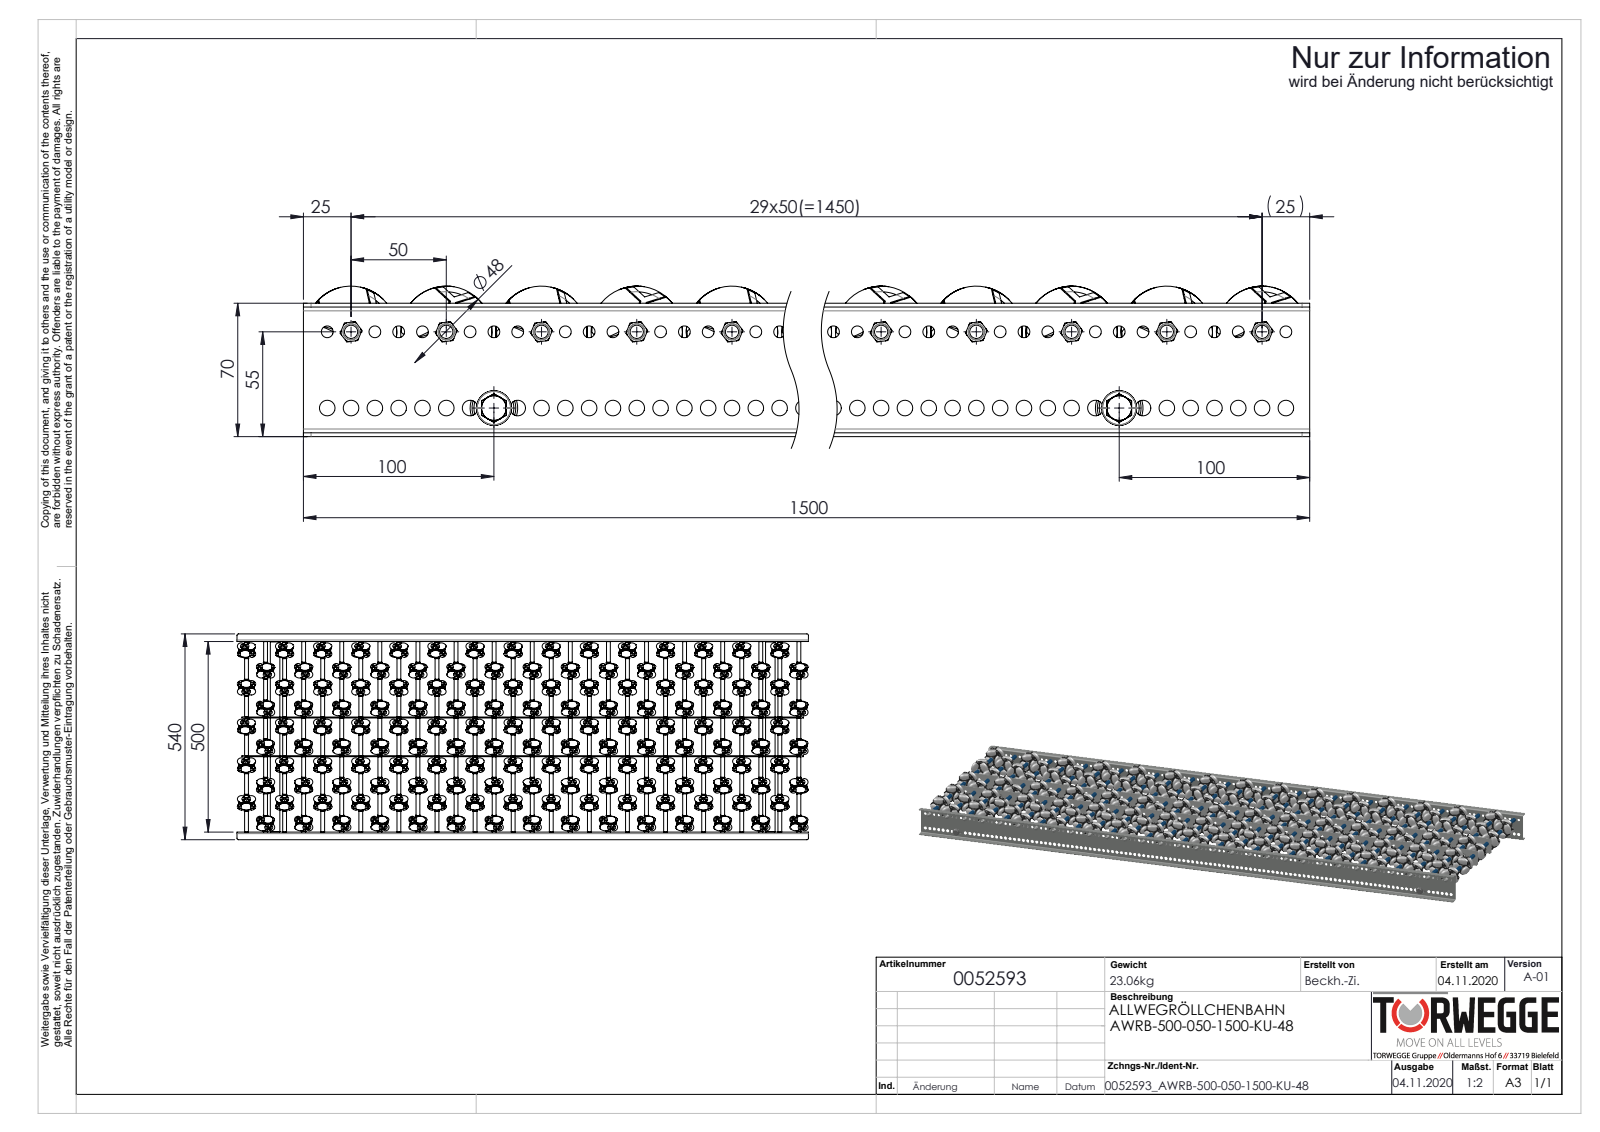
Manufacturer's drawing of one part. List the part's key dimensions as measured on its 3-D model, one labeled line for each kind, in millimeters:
Part name (STEP PRODUCT): AWR48_Röllchen; 0019719_Gewindestange-M6_L=520; 0019730_Tragrollenrohr-Ø10x1,75KU_KFG_0019730_L=54; AWR-Achse-für-Konfiguration_L500 (+8 more)
STEP written by: SolidWorks 2020 (AUTOMOTIVE_DESIGN)
Units: millimetres
Bodies: 2504 solids, 44268 faces (15372 planar, 17152 cylindrical, 11744 other)
Overall size (bounding box): 1500 × 540 × 79
Volume: 8 257 000 mm³ · Surface area: 5 570 000 mm²
Round holes (diameter × count): ⌀3.7 ×900, ⌀4.2 ×900, ⌀6.2 ×119, ⌀8.2 ×119, ⌀6.5 ×59, ⌀4.92 ×30, ⌀8.4 ×30, ⌀6.8 ×2, ⌀21 ×2
Round bosses / shafts (diameter × count): ⌀4 ×900, ⌀3.7 ×781, ⌀8 ×32, ⌀42 ×30, ⌀11 ×30, ⌀10 ×30, ⌀7 ×30, ⌀6 ×30
Partial cylindrical surfaces — rounded edges, fillets, slot ends (radius × count): R23.55 ×30, R4 ×8, R2 ×4, R5 ×4
Main face-to-face distances: 2, 502, 101.5, 2.5, 68, 500, 504, 99, 299.4, 104
Hole centre spacings: 36.06, 36.05, 36.07, 36.04, 3.1, 22.39, 4, 169.07
